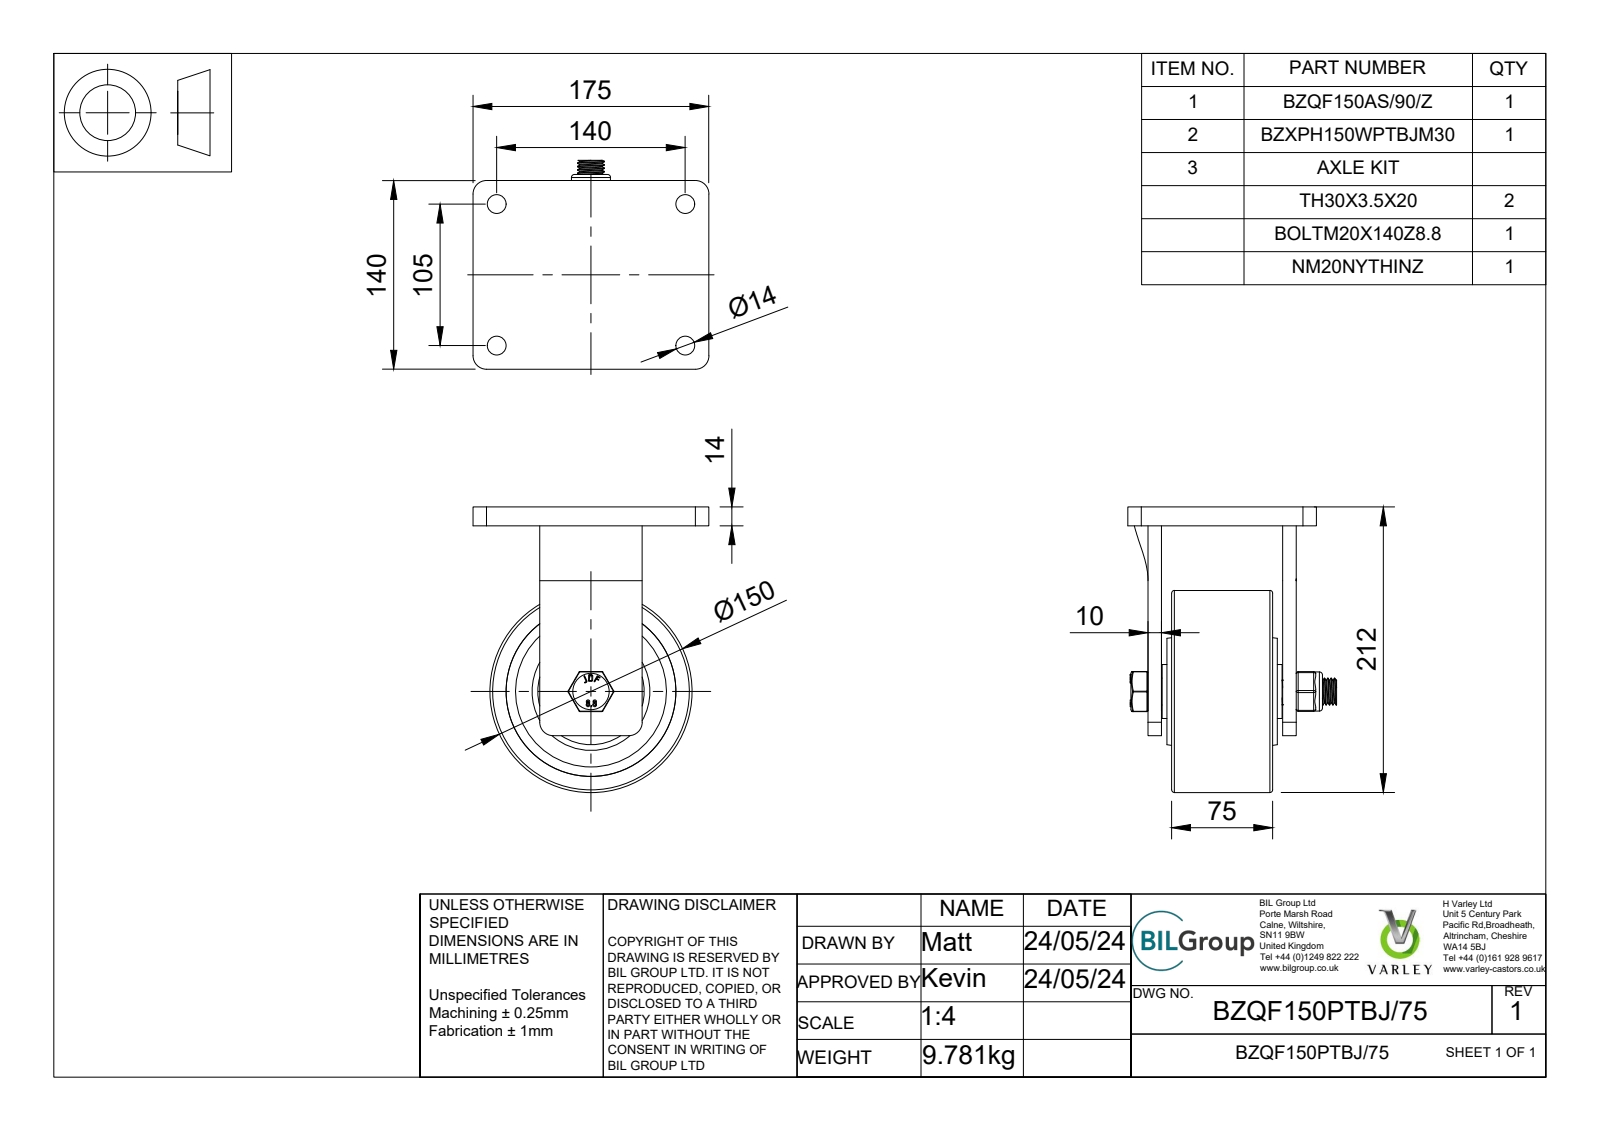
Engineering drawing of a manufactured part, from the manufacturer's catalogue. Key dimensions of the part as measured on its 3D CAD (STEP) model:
Part name (STEP PRODUCT): BZQF150PTBJ/75 v3; BZQF150AS90Z v1; FABRICATED STEEL BRACKET; BZXPH150WPTBJM30 v1 (+8 more)
STEP written by: Autodesk Translation Framework v13.14.0.145 (AUTOMOTIVE_DESIGN)
Units: millimetres
Bodies: 36 solids, 861 faces (282 planar, 269 cylindrical, 310 other)
Overall size (bounding box): 212 × 175 × 155
Volume: 1 597 000 mm³ · Surface area: 374 768 mm²
Round holes (diameter × count): ⌀7.5 ×18, ⌀14 ×4, ⌀20 ×1, ⌀20.5 ×1, ⌀30 ×1, ⌀41 ×1, ⌀45.42 ×1, ⌀51.5 ×1, ⌀55 ×1, ⌀62 ×1, ⌀112 ×1, ⌀126 ×1
Round bosses / shafts (diameter × count): ⌀150 ×1, ⌀53 ×1, ⌀49.42 ×1, ⌀42.5 ×1, ⌀40.5 ×1, ⌀40 ×1, ⌀39 ×1, ⌀36 ×1
Partial cylindrical surfaces — rounded edges, fillets, slot ends (radius × count): R1.5 ×18, R5.75 ×18, R0.5 ×12, R10 ×6, R0.66 ×4, R1.28 ×4, R0.88 ×2, R1.26 ×2
Main face-to-face distances: 14, 17.5, 10, 100, 62.5, 92.5, 7.5, 82.5, 45, 30
Hole centre spacings: 66, 105, 140, 175
